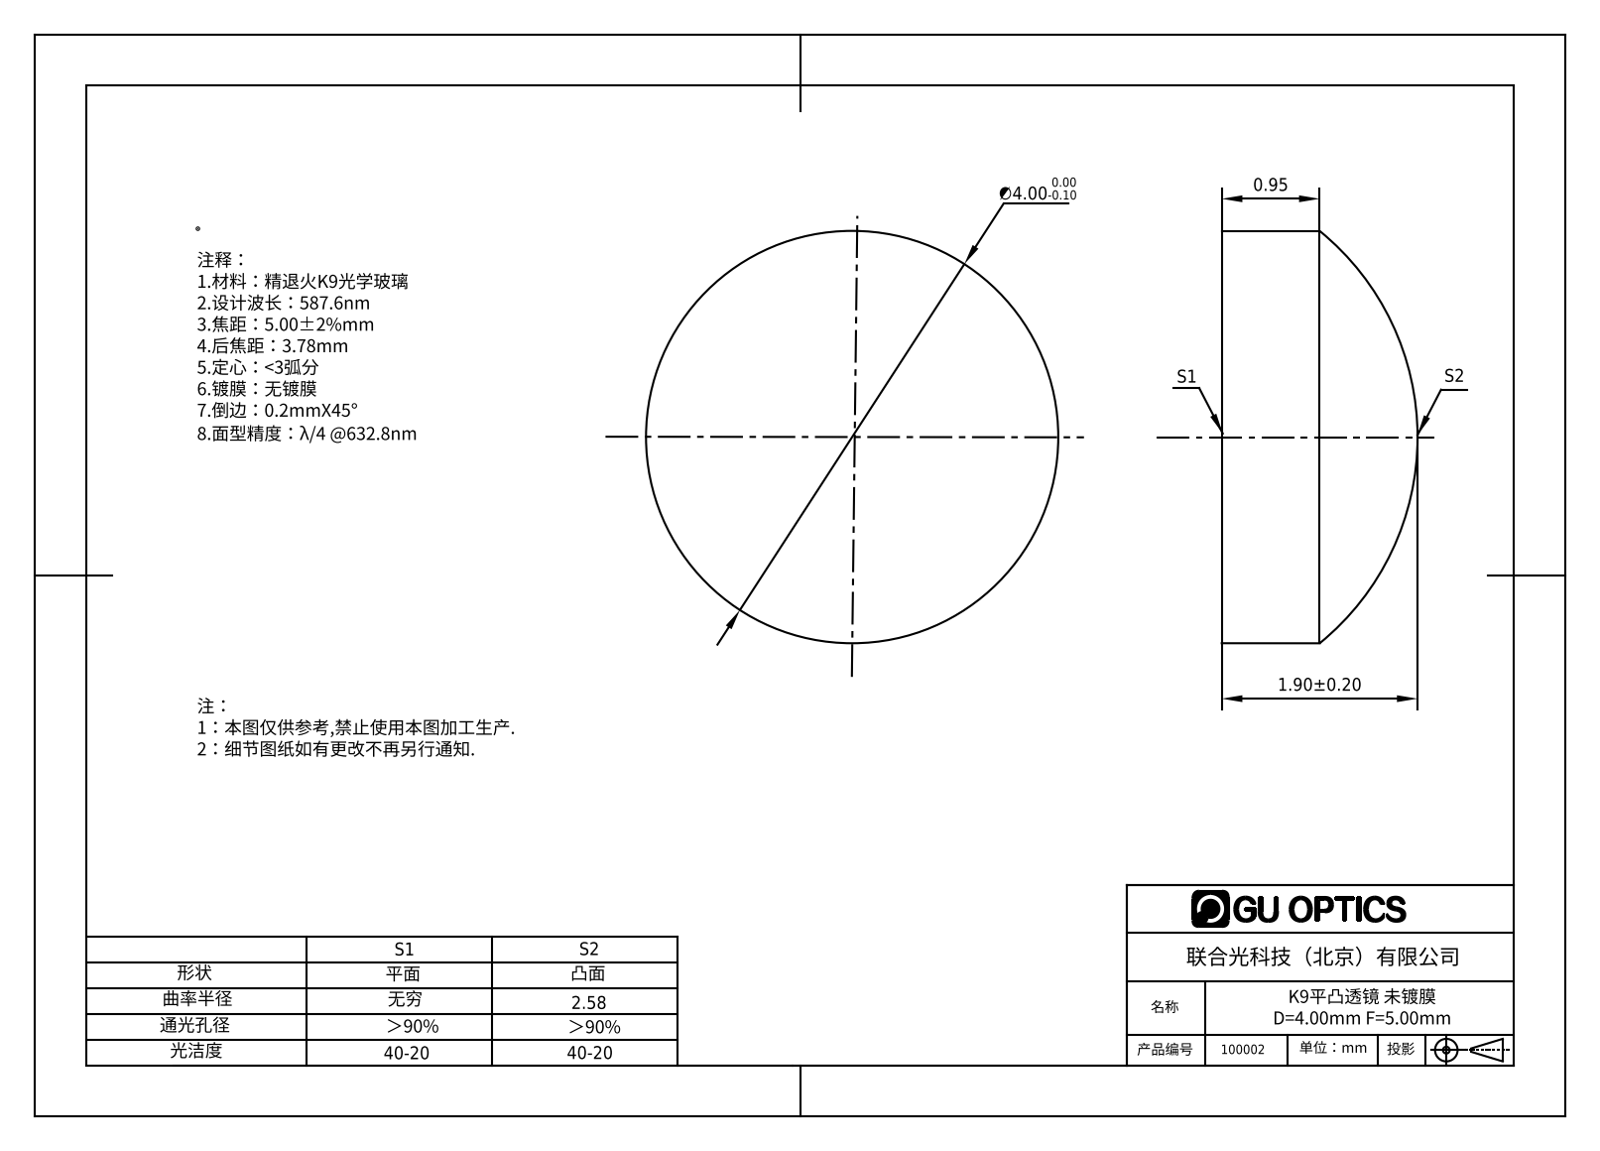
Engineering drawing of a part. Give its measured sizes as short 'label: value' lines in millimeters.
name: 100002
written by: SolidWorks 2016 (AUTOMOTIVE_DESIGN)
unit: mm
bodies: 1 solid, 5 faces (1 planar, 2 cylindrical, 2 other)
size: 4 × 4 × 1.9
volume: 18 mm³; area: 40 mm²
bosses: 1× ⌀4
